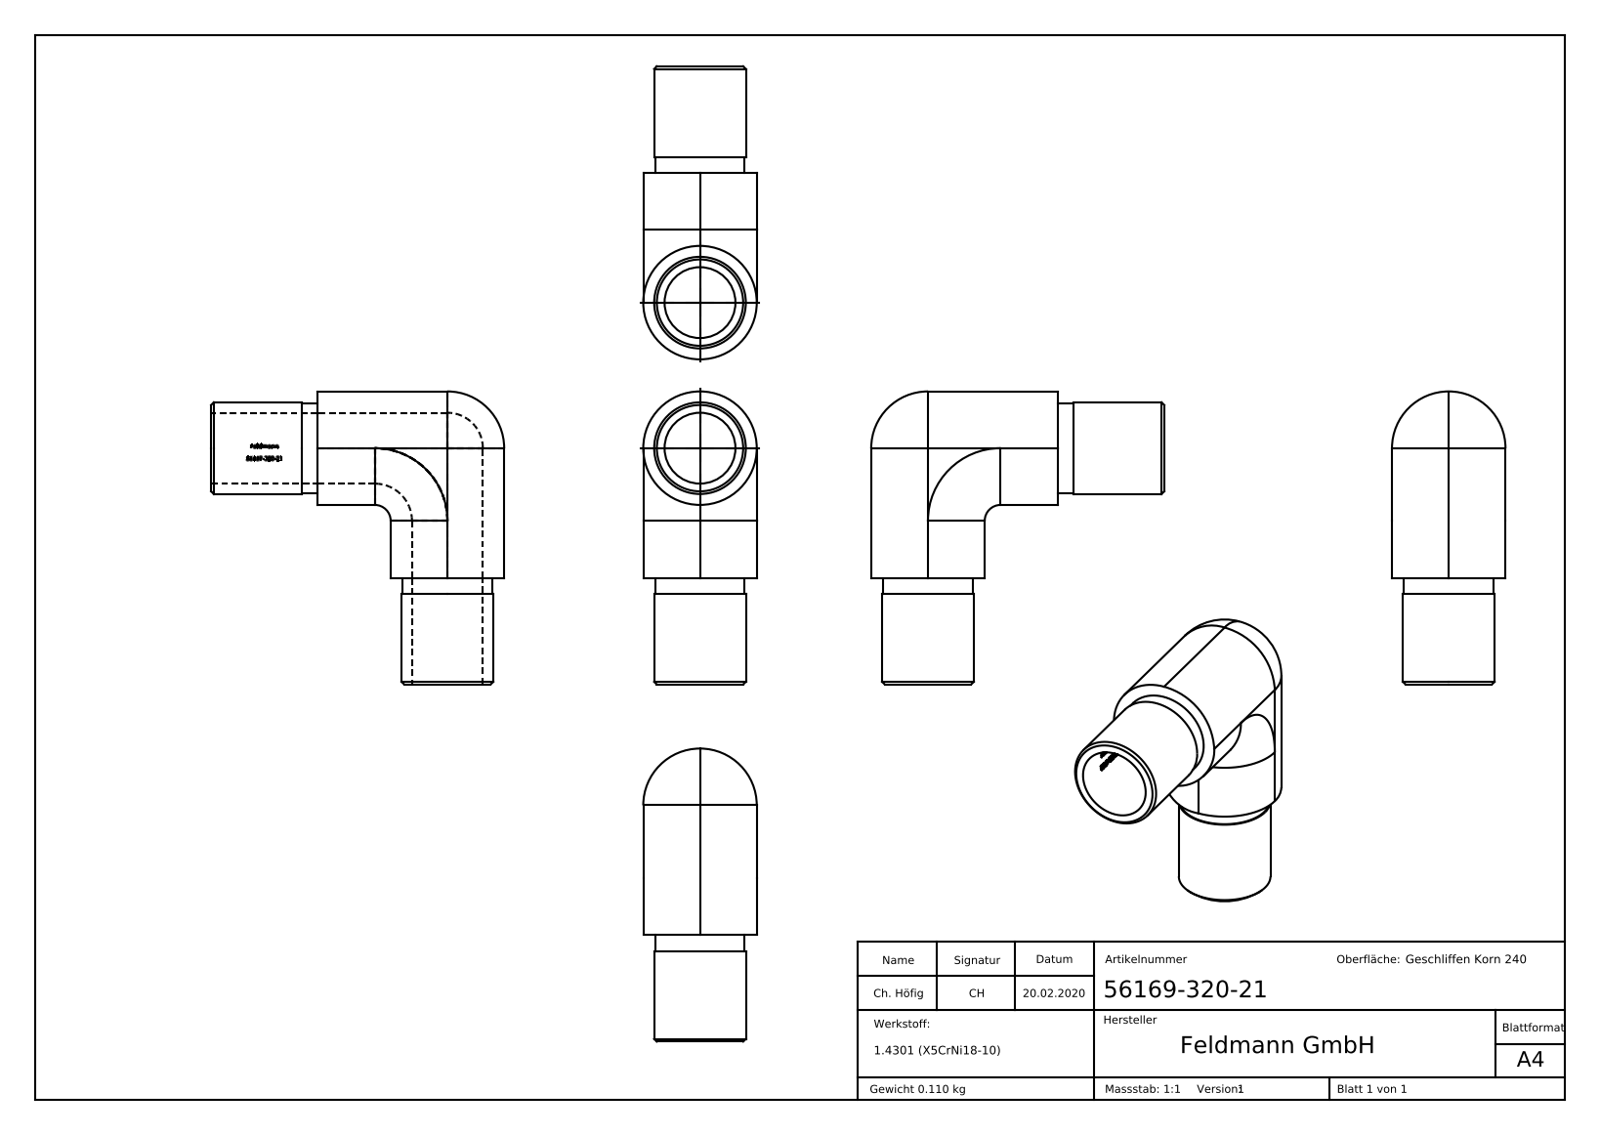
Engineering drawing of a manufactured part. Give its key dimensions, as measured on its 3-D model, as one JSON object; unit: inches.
{"part_name": "56169-320-21", "step_written_by": "SolidWorks 2015 (CONFIG_CONTROL_DESIGN)", "units": "inches", "bodies": {"solids": 1, "faces": 283, "planar": 114, "cylindrical": 41, "other": 128}, "overall_size": [2.165, 2.165, 0.839], "volume_in3": 0.85, "surface_area_in2": 14.59, "round_holes": [[0.524, 2]], "round_bosses_or_shafts": [[0.839, 2], [0.677, 2], [0.661, 2]], "partial_cylinders_radius": [[0.266, 1]], "face_to_face_distances": [0.787, 0.157, 0.681, 0.839, 0.524, 0.118, 0.669, 0.109, 0.197, 0.175]}
